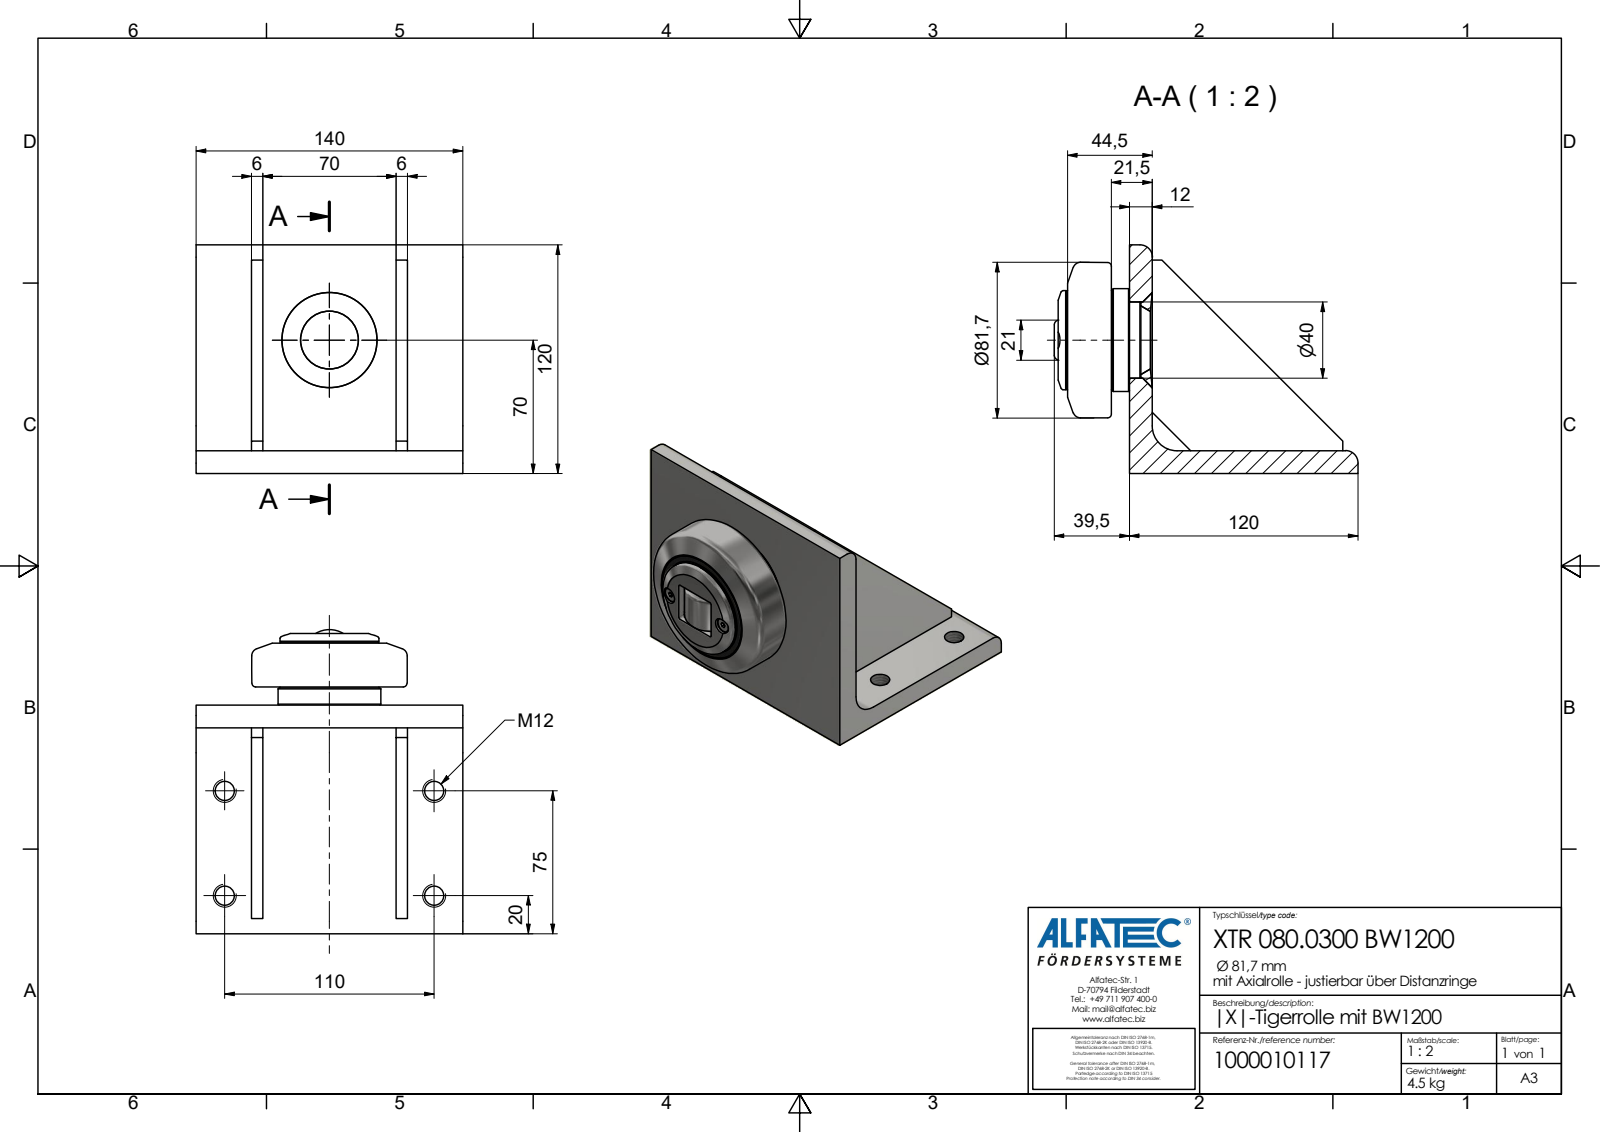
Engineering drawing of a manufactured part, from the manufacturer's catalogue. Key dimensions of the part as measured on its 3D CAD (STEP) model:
Part name (STEP PRODUCT): XTR 080.0300 BW1200_Kontur
STEP written by: Autodesk Inventor 2020 (AP242_MANAGED_MODEL_BASED_3D_ENGINEERING_MIM_LF)
Units: millimetres
Bodies: 1 solid, 115 faces (60 planar, 34 cylindrical, 21 other)
Overall size (bounding box): 159.5 × 140 × 120
Volume: 589 506 mm³ · Surface area: 109 343 mm²
Round holes (diameter × count): ⌀10.11 ×4, ⌀4.5 ×2, ⌀8.6 ×2, ⌀46.2 ×1
Round bosses / shafts (diameter × count): ⌀7.8 ×2, ⌀4 ×2, ⌀54 ×1, ⌀52 ×1, ⌀32.8 ×1
Partial cylindrical surfaces — rounded edges, fillets, slot ends (radius × count): R1 ×4, R6.5 ×2, R8 ×1, R9 ×1, R10.5 ×1, R13 ×1
Main face-to-face distances: 12, 76, 6, 29, 35, 105, 111, 82, 70, 140
Hole centre spacings: 19.5, 55, 110, 122.98, 39
